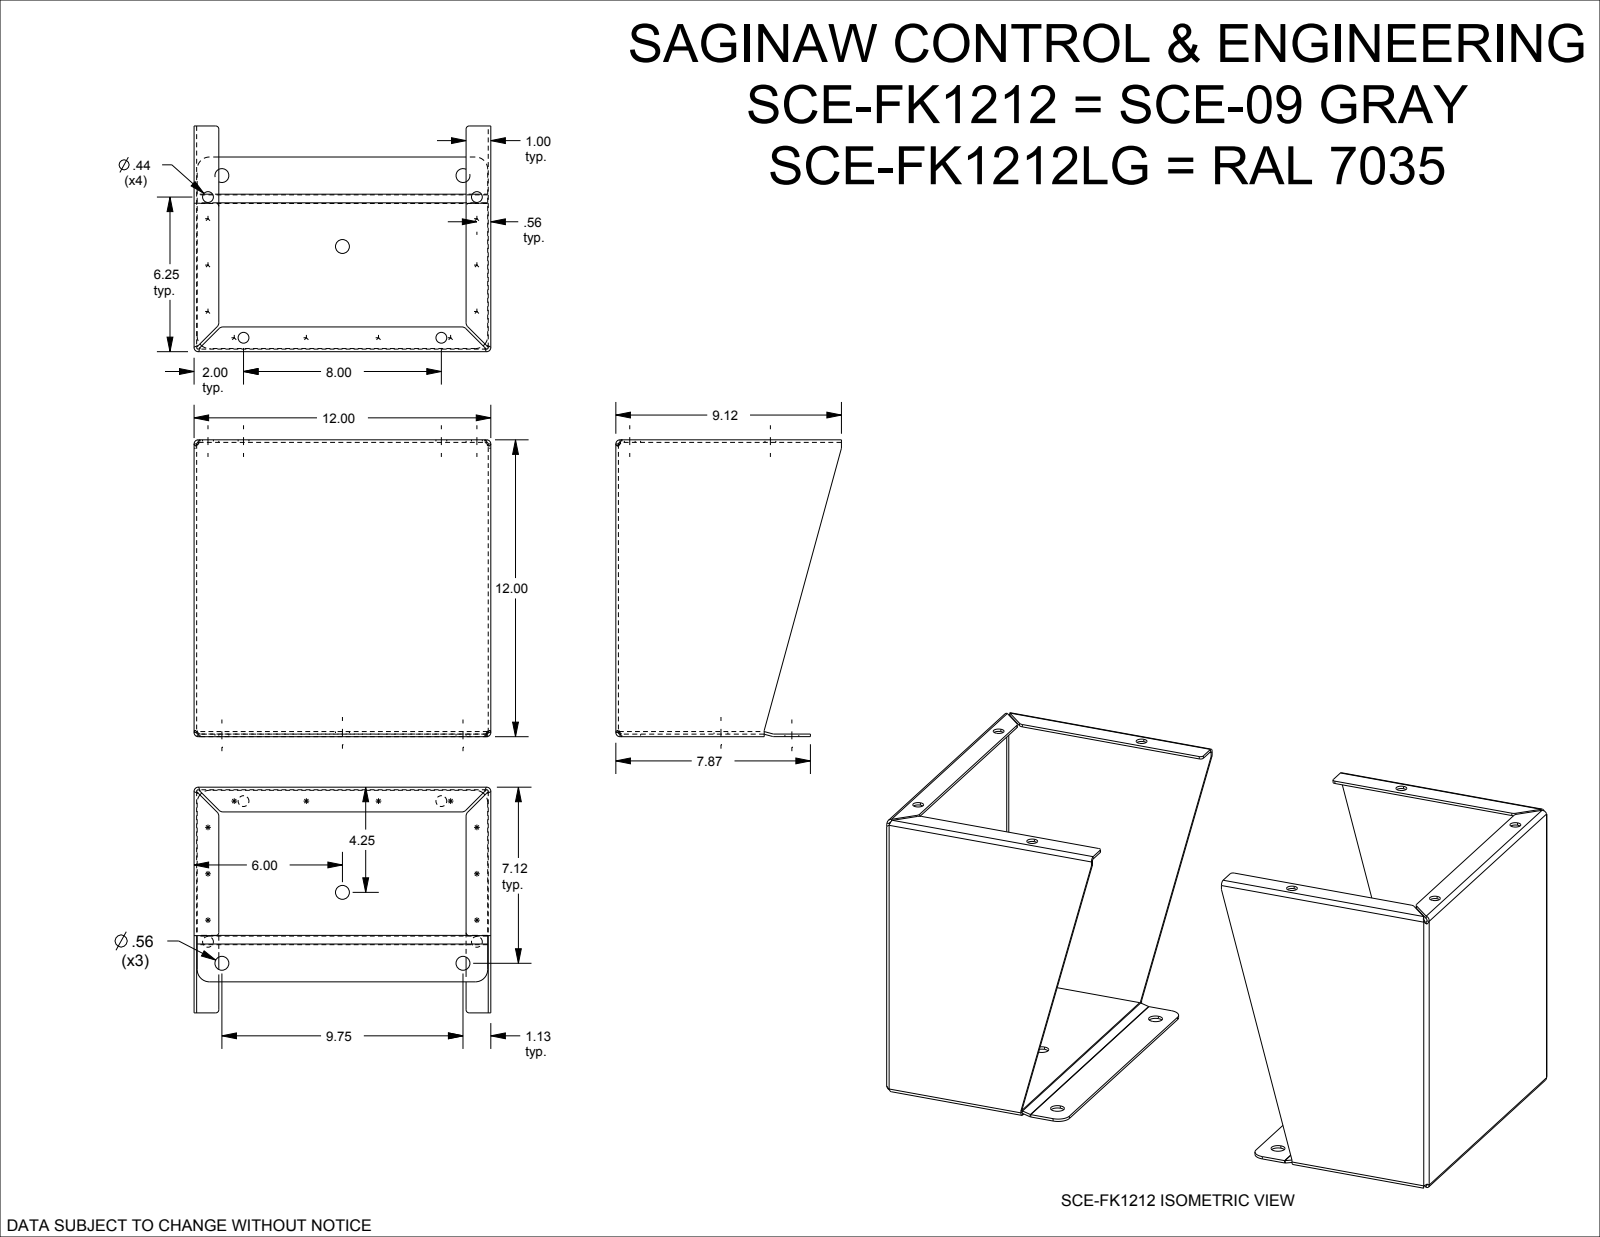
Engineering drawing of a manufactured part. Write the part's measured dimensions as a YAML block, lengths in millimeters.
part_name: "SCE-FK1212"
step_written_by: "SolidWorks 2019 (CONFIG_CONTROL_DESIGN)"
units: millimeters
bodies: {solids: 4, faces: 214, planar: 96, cylindrical: 86, other: 32}
overall_size: [609.6, 304.8, 304.8]
volume: 1544000
surface_area: 1187000
round_holes:
  - {diameter: 11.1, count: 8}
  - {diameter: 14.3, count: 6}
partial_cylinders:
  - {radius: 4.2, count: 16}
  - {radius: 1.6, count: 12}
  - {radius: 3.2, count: 8}
  - {radius: 5.6, count: 8}
  - {radius: 12.7, count: 8}
  - {radius: 1.6, count: 4}
face_to_face_distances: [2.6, 302.2, 607, 299.5, 304.8, 609.6, 604.3, 2.6, 302.1, 296.9]
hole_center_spacings: [26.3, 138.2, 143.7, 147.1, 149, 168, 270.4, 279.9]
